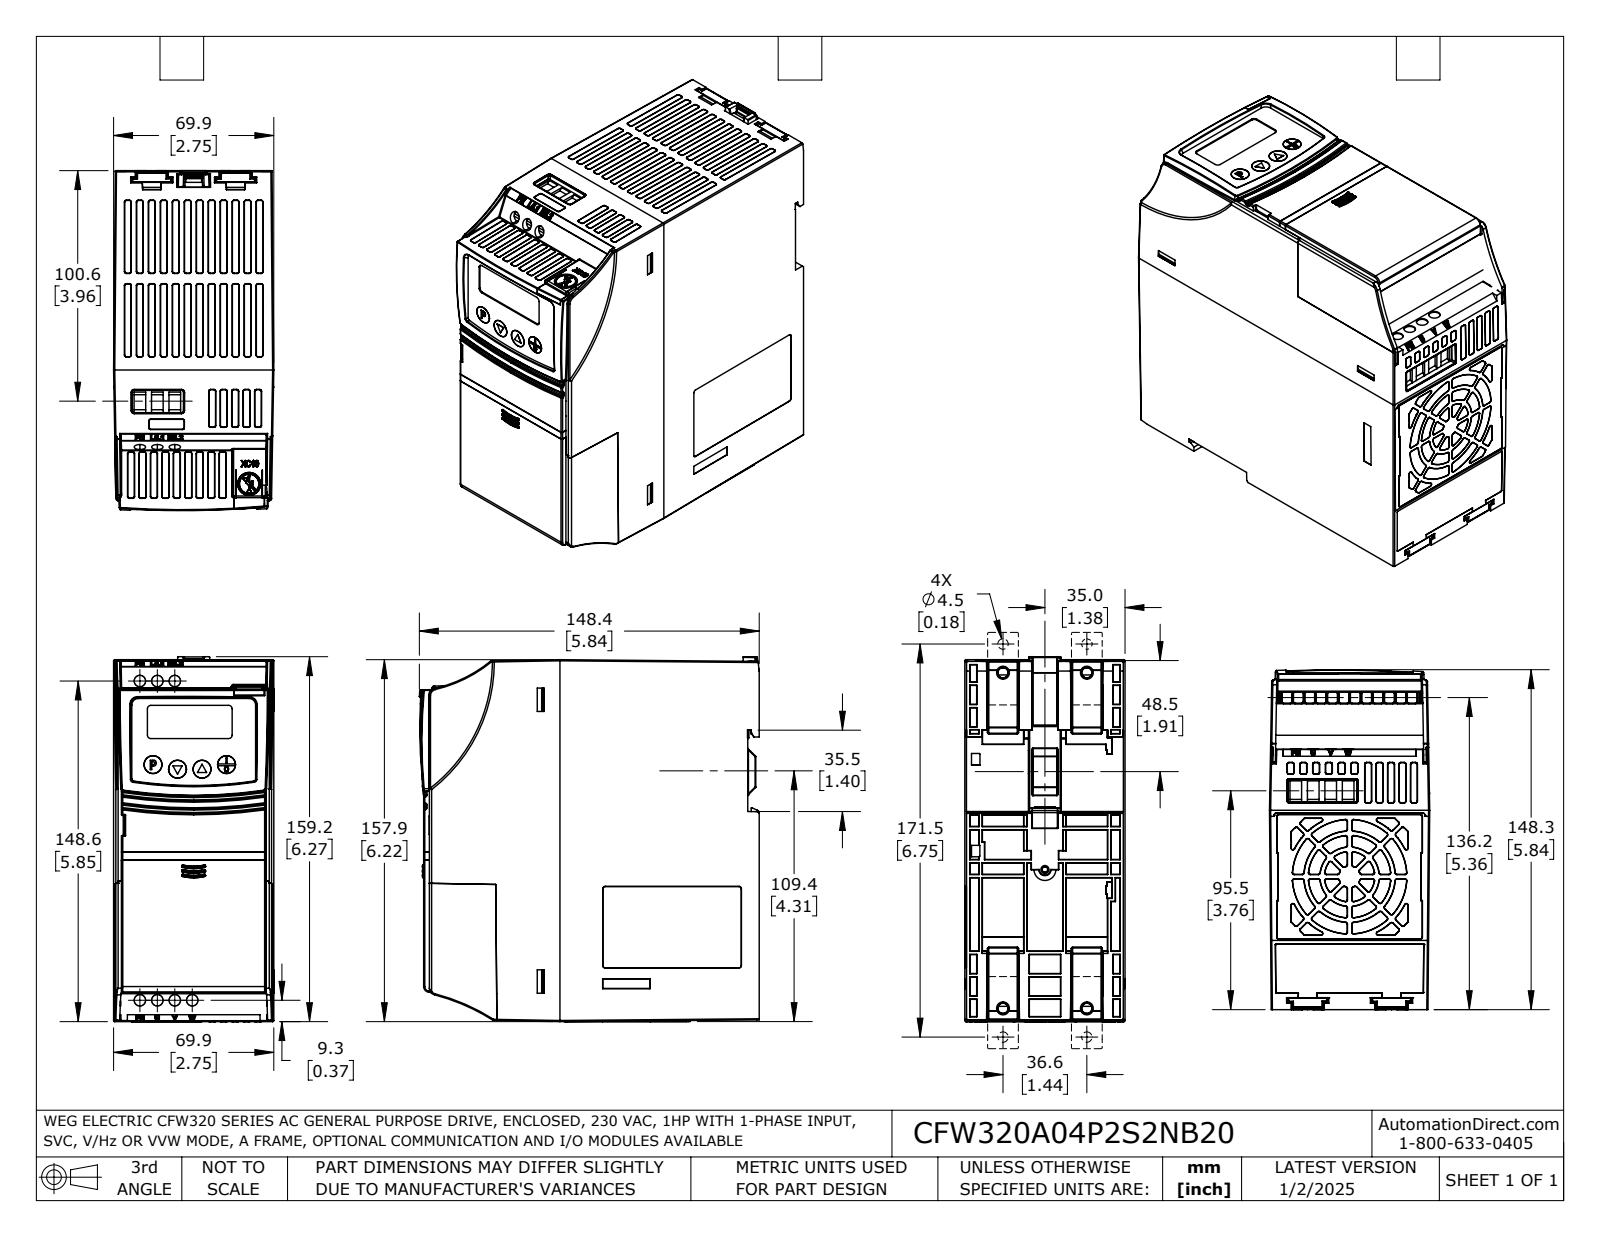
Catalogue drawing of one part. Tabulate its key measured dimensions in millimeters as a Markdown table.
| quantity | value |
| --- | --- |
| part name | CFW320A04P2S2NB20 |
| STEP written by | SolidWorks 2021 (AUTOMOTIVE_DESIGN) |
| units | millimeters |
| bodies | 6 solids, 3715 faces (1587 planar, 853 cylindrical, 1275 other) |
| overall size | 159.2 × 148.4 × 70 |
| volume | 249 700 mm³ |
| surface area | 199 400 mm² |
| round holes (diameter × count) | 5 × 3 |
| partial cylindrical surfaces (radius × count) | 0.3 × 327, 0.5 × 150, 1 × 13, 0.8 × 5, 3 × 3, 0.3 × 2, 2.5 × 1, 3.2 × 1 |
| main face-to-face distances | 1.8, 1.4, 0.5, 1.3, 152.4, 135.4, 134, 141.5, 140.1, 6.1 |
| hole center spacings | 7.6, 15.2 |
